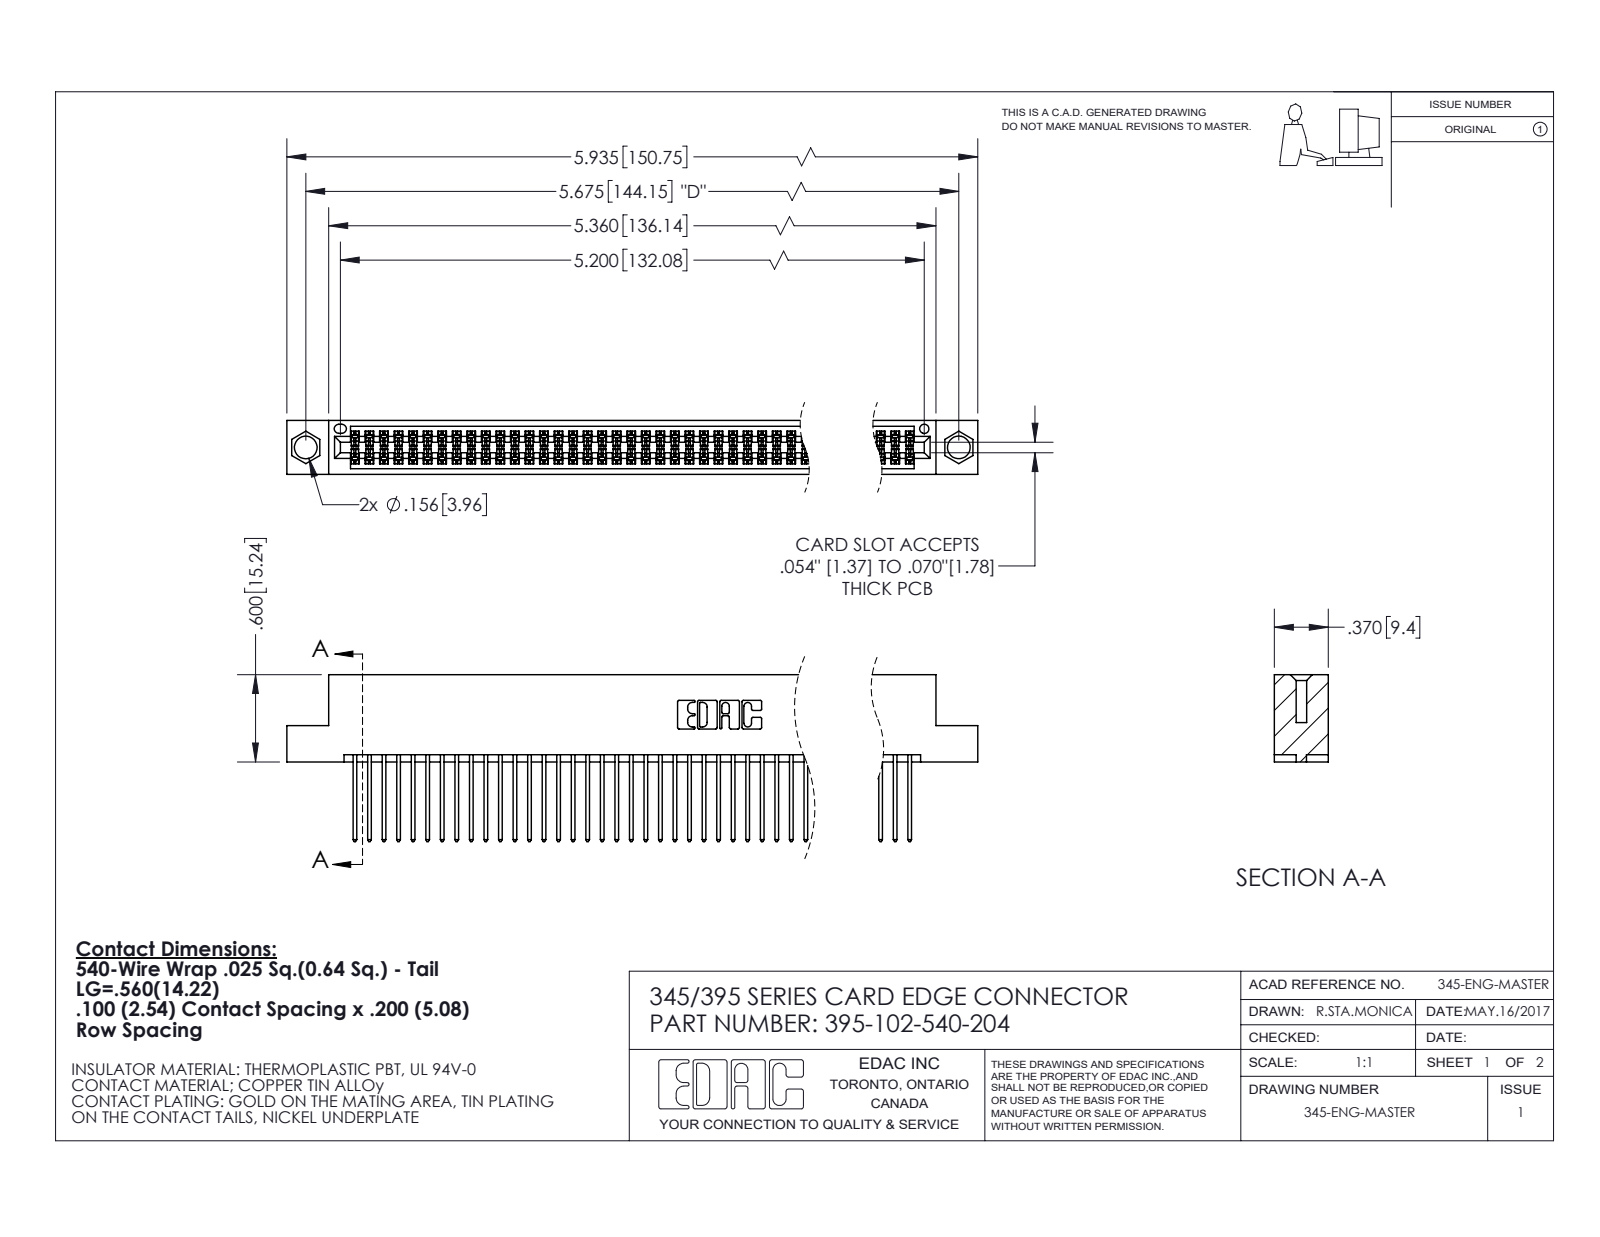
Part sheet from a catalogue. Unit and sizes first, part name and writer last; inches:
Units: inches
Overall size (bounding box): 5.935 × 1.147 × 0.37
Round holes (diameter × count): ⌀0.156 ×2, ⌀0.064 ×1
Partial cylindrical surfaces — rounded edges, fillets, slot ends (radius × count): R0.006 ×204, R0.01 ×102, R0.01 ×22, R0.007 ×6, R0.031 ×6, R0.026 ×3, R0.014 ×2, R0.019 ×2
Main face-to-face distances: 0.298, 0.072, 0.2, 0.098, 0.272, 0.025, 0.37, 0.225, 0.175, 0.149
Hole centre spacings: 0.27, 5.439, 5.675
Volume: 0.916 in³ · Surface area: 37.21 in²
Bodies: 103 solids, 5240 faces (3460 planar, 1780 cylindrical, 0 other)
Part name (STEP PRODUCT): 345 Part_Flush Mounting Lugs - 0.156 Dia-TI; 345-292-001_345-293-140; 395-102-540-204
STEP written by: SolidWorks 2020 (CONFIG_CONTROL_DESIGN)
